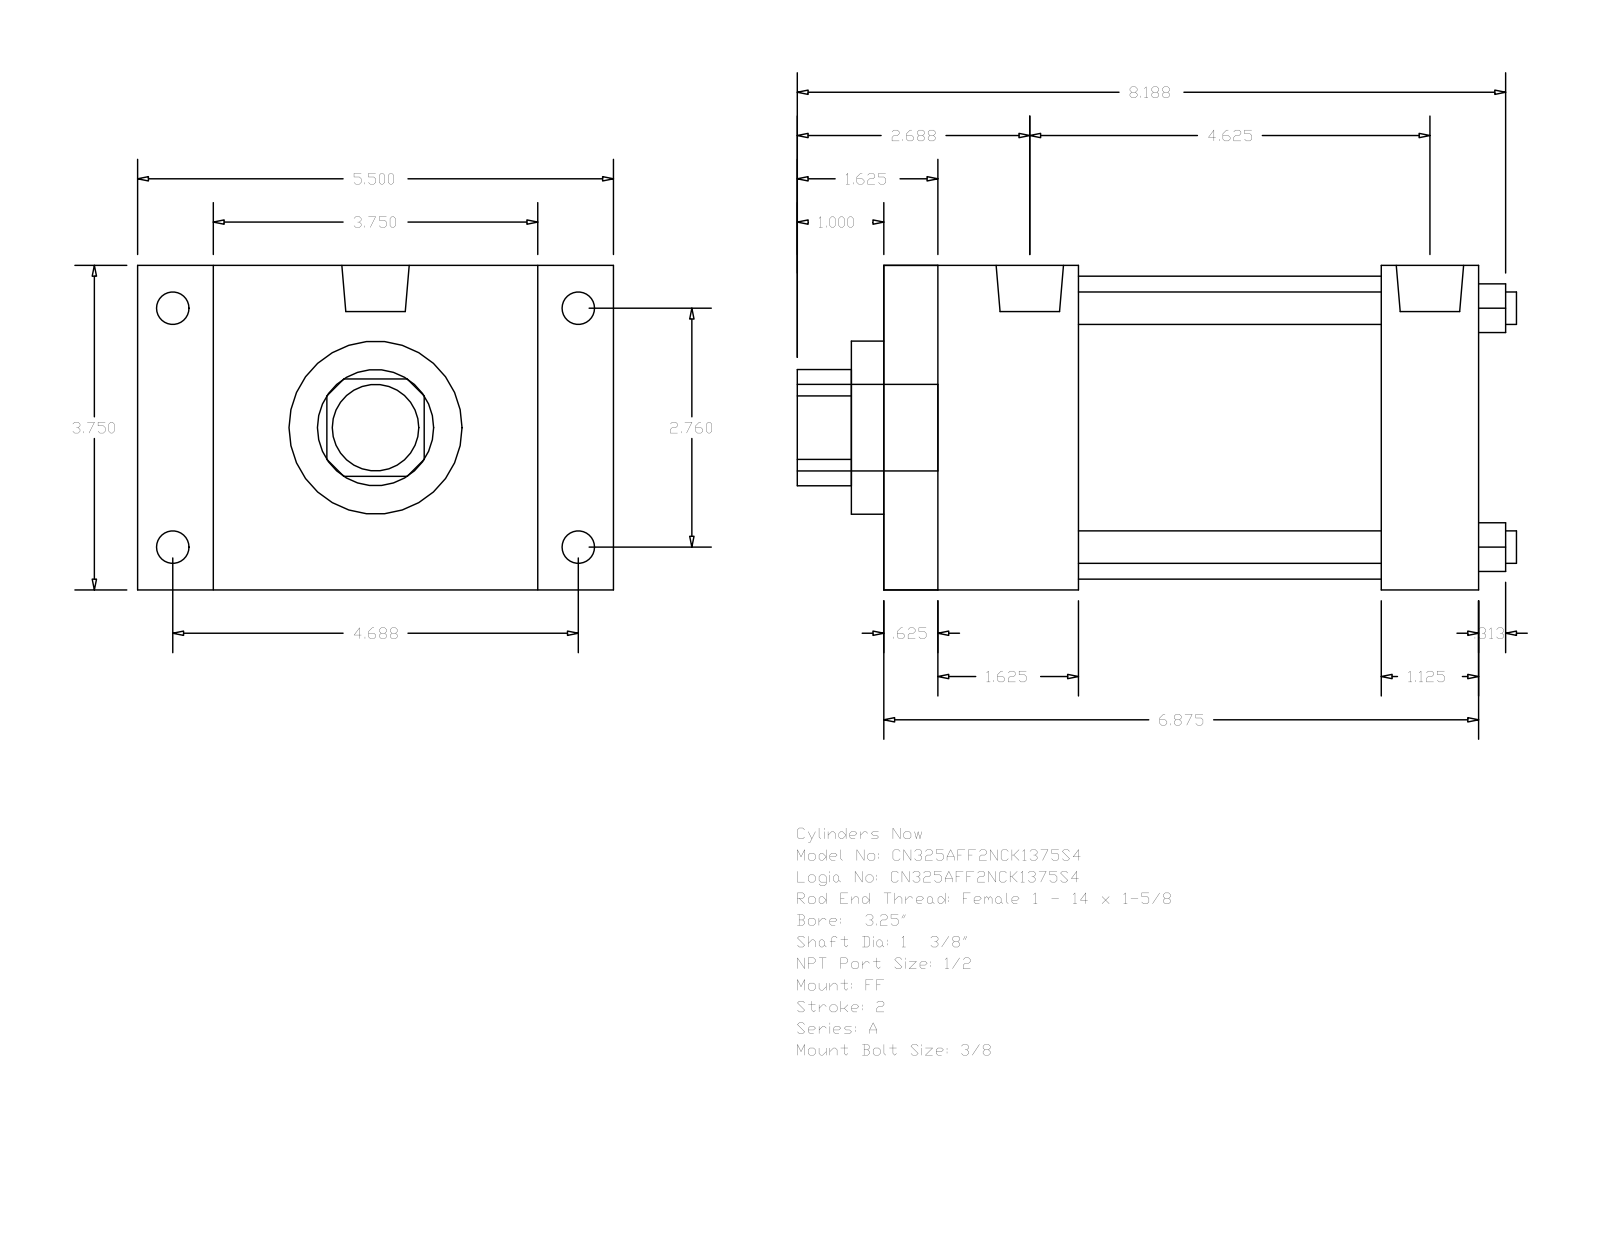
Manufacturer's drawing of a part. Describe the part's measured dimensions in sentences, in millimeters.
The part is named "A_FF__0325_1.375". Its 3-D file was written by "GSSL Pune (CONFIG_CONTROL_DESIGN)". It is 0 solids with 92 faces: 64 planar, 28 cylindrical and 0 other. Overall it measures 211.14 by 139.7 by 95.25 millimeters. Round holes: 4 of diameter 9.53, 1 of diameter 34.92, 1 of diameter 50.8, 1 of diameter 88.9. Round bosses or shafts: 4 of diameter 9.53, 4 of diameter 8.73, 2 of diameter 19.77, 1 of diameter 25.4. Partial cylindrical surfaces (rounded edges, fillets, slot ends): 1 of radius 17.06. The main face-to-face distances are 95.24, 174.63, 15.87, 158.76, 28.58, 22.23, 117.47, 57.15, 146.05, 41.28. The hole center spacings are 49.57, 70.1, 99.14.
